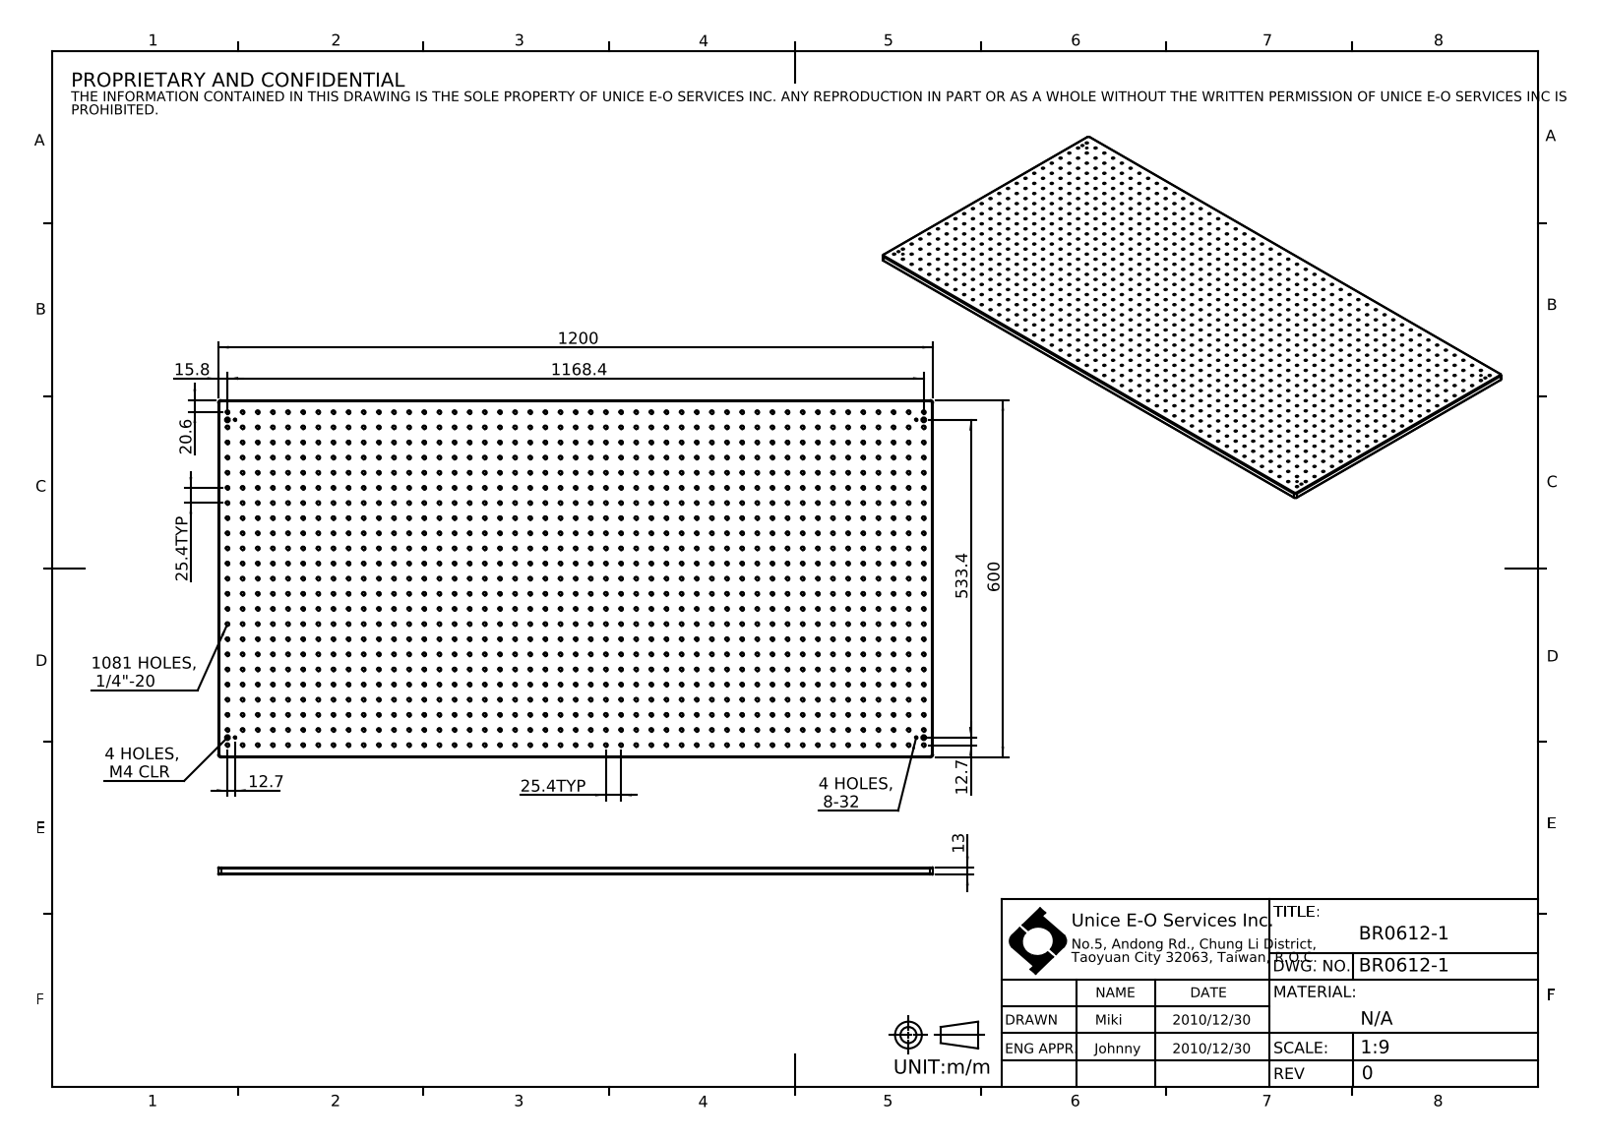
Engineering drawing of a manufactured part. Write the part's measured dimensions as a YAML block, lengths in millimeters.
part_name: "BR0612-1"
step_written_by: "SolidWorks 2016 (CONFIG_CONTROL_DESIGN)"
units: millimeters
bodies: {solids: 1, faces: 2216, planar: 10, cylindrical: 2198, other: 8}
overall_size: [1200, 600, 13]
volume: 9064000
surface_area: 1663000
round_holes:
  - {diameter: 5.11, count: 1081}
  - {diameter: 3.45, count: 4}
  - {diameter: 4.5, count: 4}
  - {diameter: 8, count: 4}
partial_cylinders:
  - {radius: 2, count: 8}
  - {radius: 5, count: 4}
face_to_face_distances: [13, 600, 1200, 7, 6]
hole_center_spacings: [25.4, 50.8, 76.2, 101.6, 127, 152.4, 177.8, 203.2]
